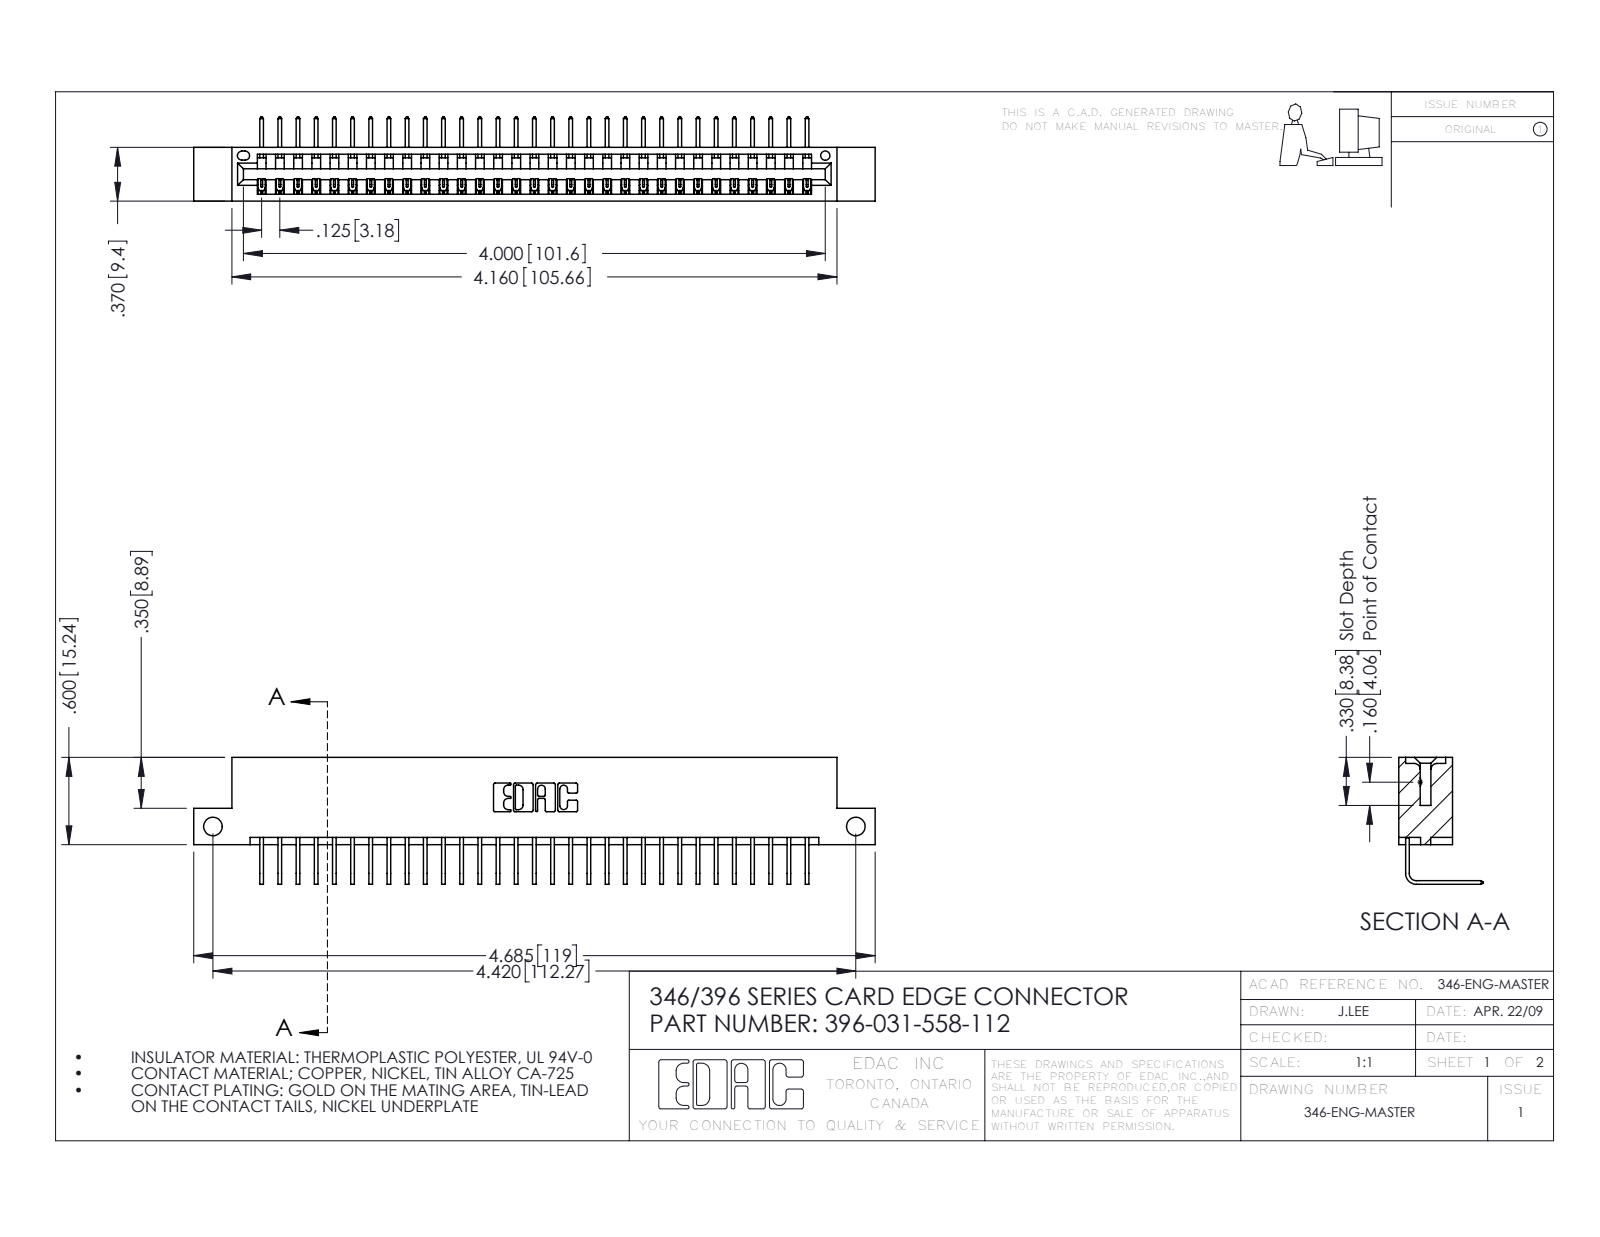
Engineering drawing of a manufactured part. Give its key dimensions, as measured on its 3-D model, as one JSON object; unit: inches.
{"part_name": "396-031-558-112; 345-292-001_558 Tail - 2; 346 Part_Flush Mounting Lugs - Side Mount", "step_written_by": "SolidWorks 2016 (CONFIG_CONTROL_DESIGN)", "units": "inches", "bodies": {"solids": 32, "faces": 1982, "planar": 1378, "cylindrical": 604, "other": 0}, "overall_size": [4.685, 0.873, 0.58], "volume_in3": 0.691, "surface_area_in2": 22.5, "round_holes": [[0.128, 2], [0.064, 1]], "partial_cylinders_radius": [[0.006, 62], [0.01, 22], [0.007, 6], [0.031, 6], [0.026, 3], [0.031, 2], [0.04, 2], [0.014, 1]], "face_to_face_distances": [0.322, 0.048, 0.37, 0.25, 0.298, 0.025, 0.072, 0.148, 0.222, 0.1], "hole_center_spacings": [4.42]}
